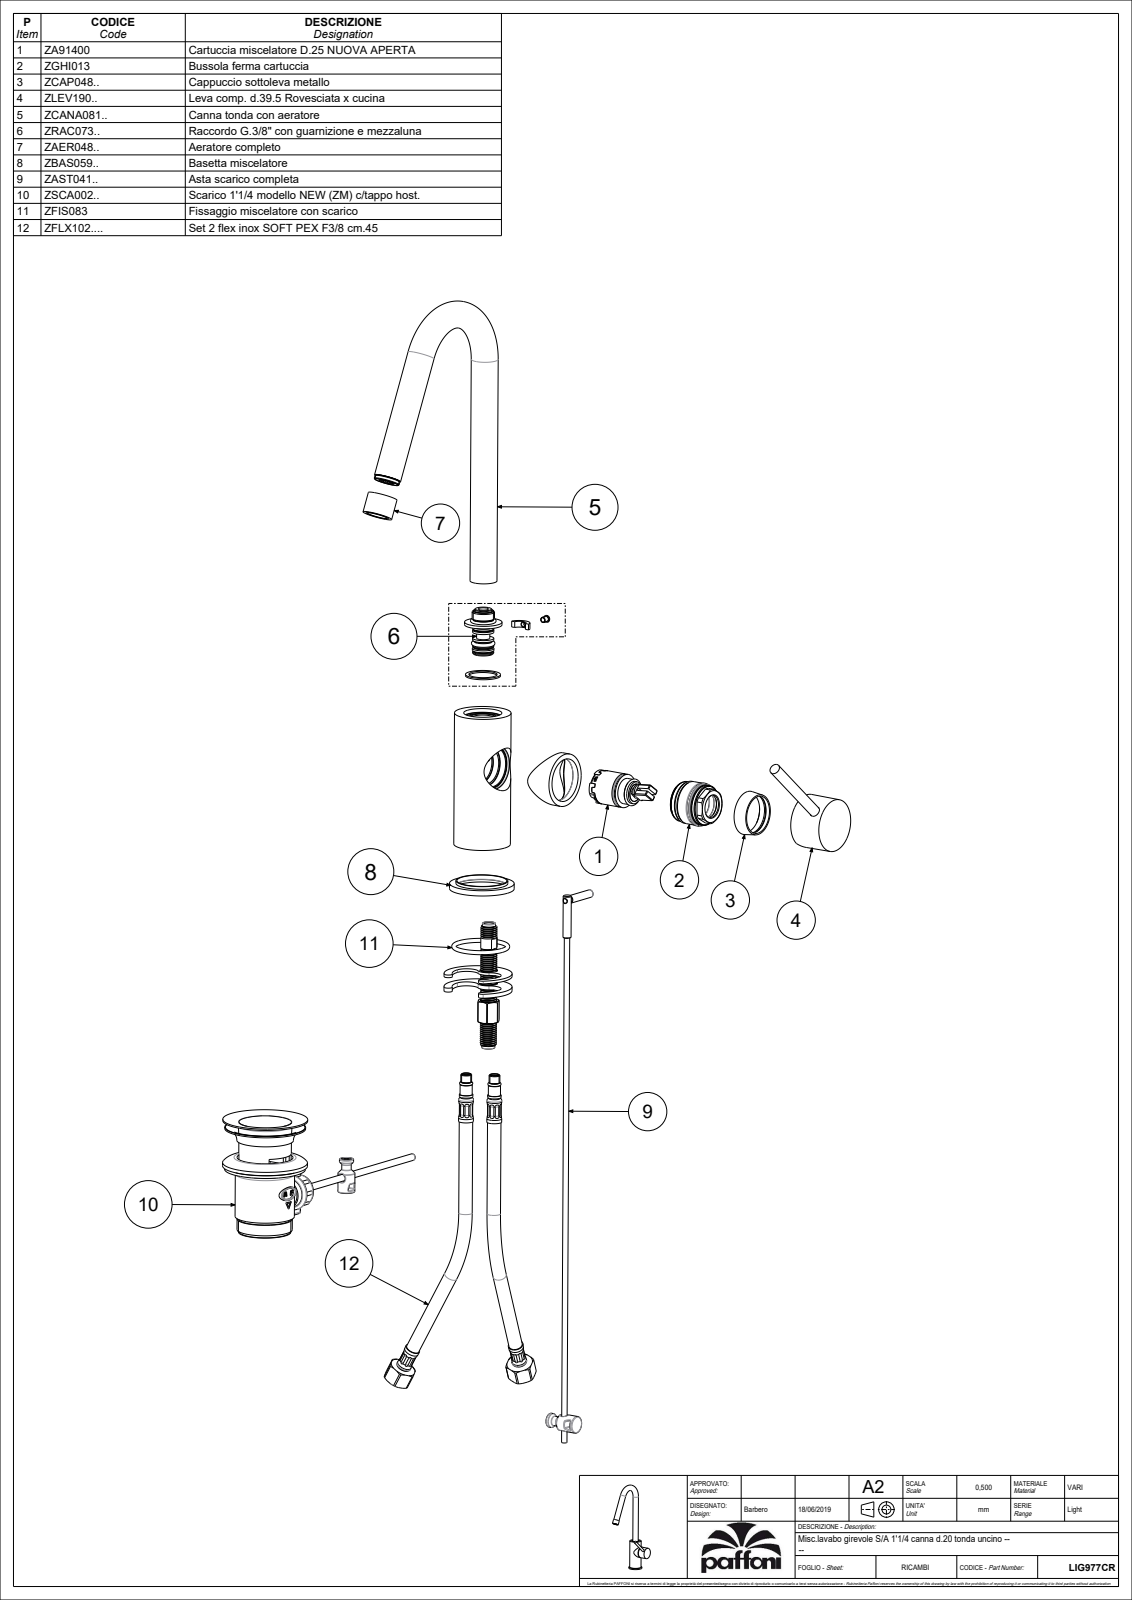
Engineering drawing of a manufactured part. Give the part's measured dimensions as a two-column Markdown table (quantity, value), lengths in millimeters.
| quantity | value |
| --- | --- |
| part name | LIG977CR |
| STEP written by | CREO PARAMETRIC BY PTC INC, 2020044 (CONFIG_CONTROL_DESIGN) |
| units | millimeters |
| bodies | 0 solids, 113 faces (44 planar, 48 cylindrical, 21 other) |
| overall size | 323.5 × 169.72 × 79.15 |
| round holes (diameter × count) | 3 × 1 |
| round bosses / shafts (diameter × count) | 20 × 2, 48 × 1, 42 × 1, 39.5 × 1, 22 × 1, 7.9 × 1, 7.6 × 1, 6 × 1 |
| partial cylindrical surfaces (radius × count) | 1 × 8, 0.8 × 2, 3.5 × 1, 5 × 1, 6.4 × 1 |
| main face-to-face distances | 4, 104, 100, 10, 25.15, 15.15, 15, 24.15, 14.15, 1 |
